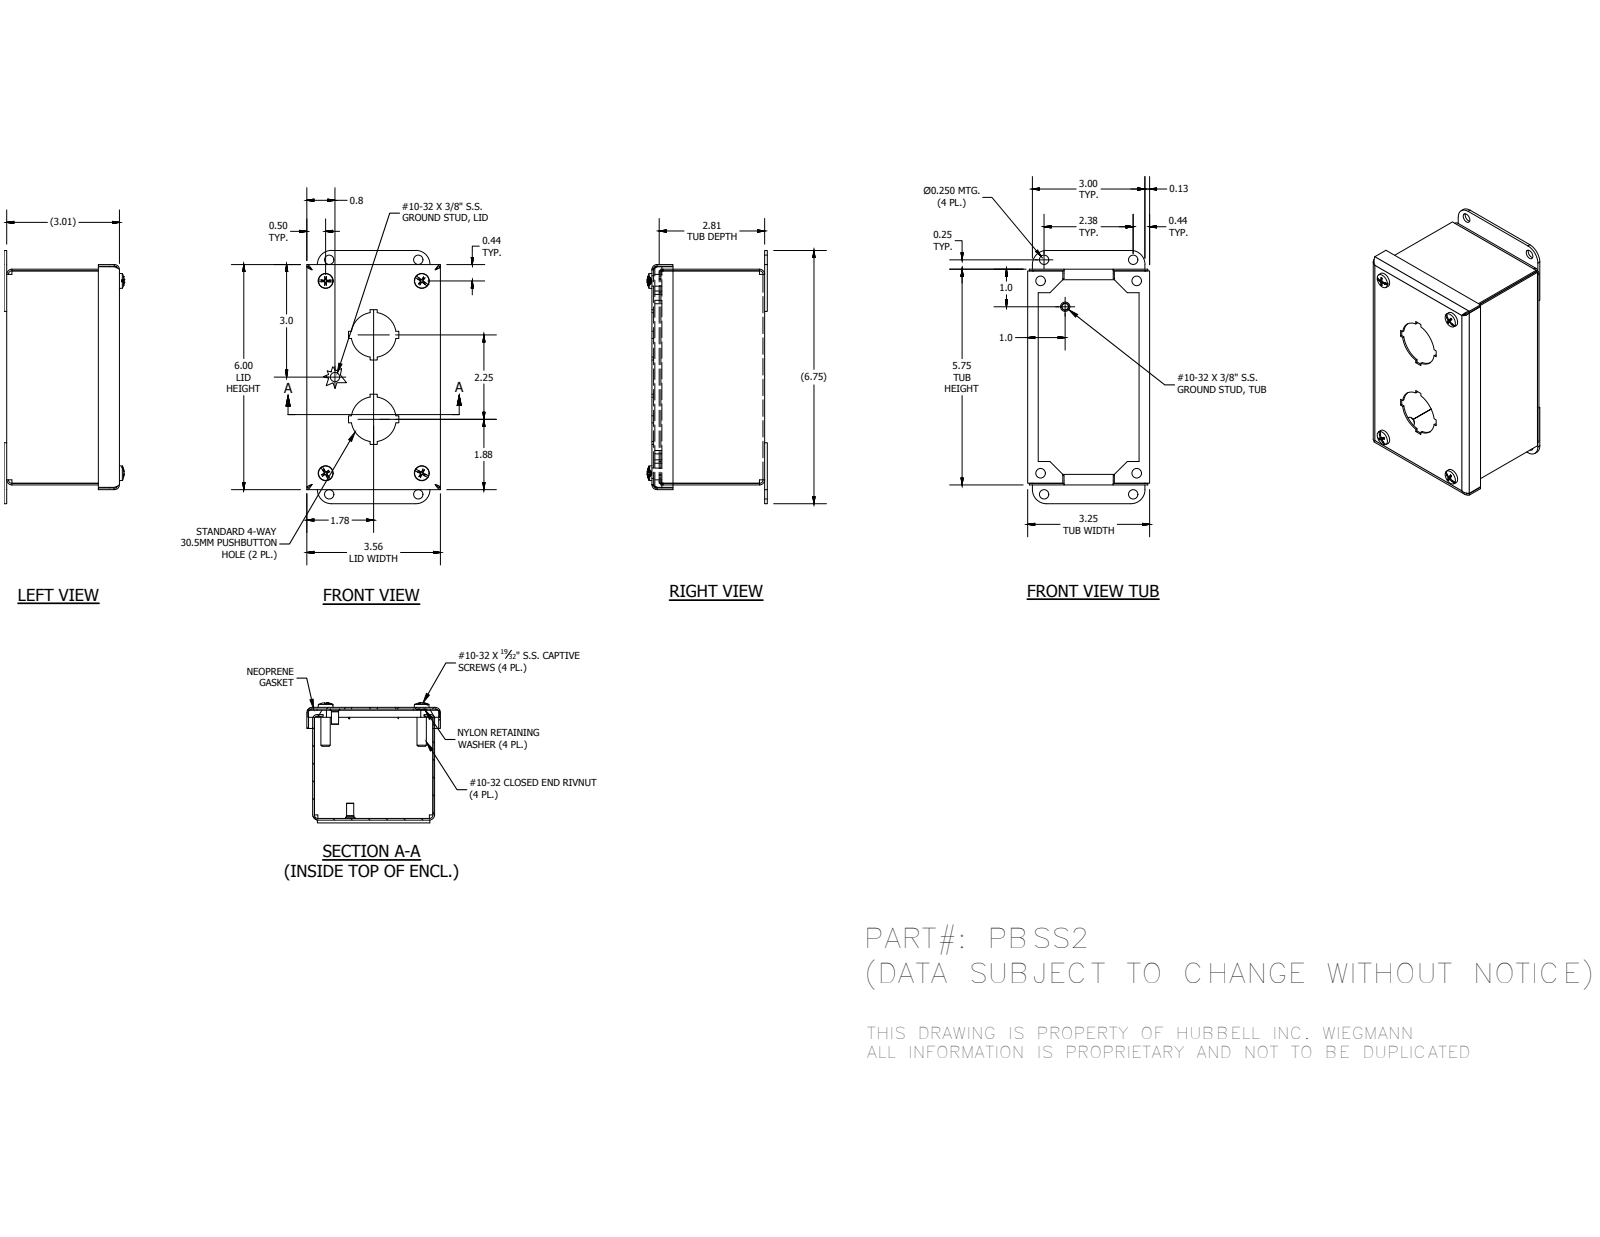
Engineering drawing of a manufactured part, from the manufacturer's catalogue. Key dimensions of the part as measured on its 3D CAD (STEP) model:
Part name (STEP PRODUCT): PBSS2LID; 37210; 39077; PBSS2BKP (+5 more)
STEP written by: Autodesk Inventor 2016 (AUTOMOTIVE_DESIGN)
Units: millimetres
Bodies: 20 solids, 568 faces (356 planar, 104 cylindrical, 108 other)
Overall size (bounding box): 171.45 × 90.49 × 81.29
Volume: 116 786 mm³ · Surface area: 165 286 mm²
Round holes (diameter × count): ⌀3.96 ×4, ⌀4.98 ×4, ⌀6.35 ×4, ⌀6.53 ×4, ⌀7.06 ×4, ⌀7.14 ×4, ⌀7.95 ×4, ⌀3.38 ×2, ⌀30.48 ×2
Round bosses / shafts (diameter × count): ⌀11.51 ×4, ⌀10.31 ×4, ⌀6.3 ×4, ⌀4.25 ×4, ⌀6.35 ×2, ⌀4.83 ×2
Partial cylindrical surfaces — rounded edges, fillets, slot ends (radius × count): R2.38 ×8, R3.52 ×8, R2.27 ×4, R9.53 ×4, R1.59 ×3, R2.73 ×3, R1.59 ×1, R2.73 ×1
Main face-to-face distances: 1.14, 1.15, 75.19, 76.33, 144.91, 75.18, 74.04, 81.4, 80.26, 82.55
Hole centre spacings: 0.48, 48.91, 99.15, 130.62, 144.48, 144.93, 14.07, 14.48
